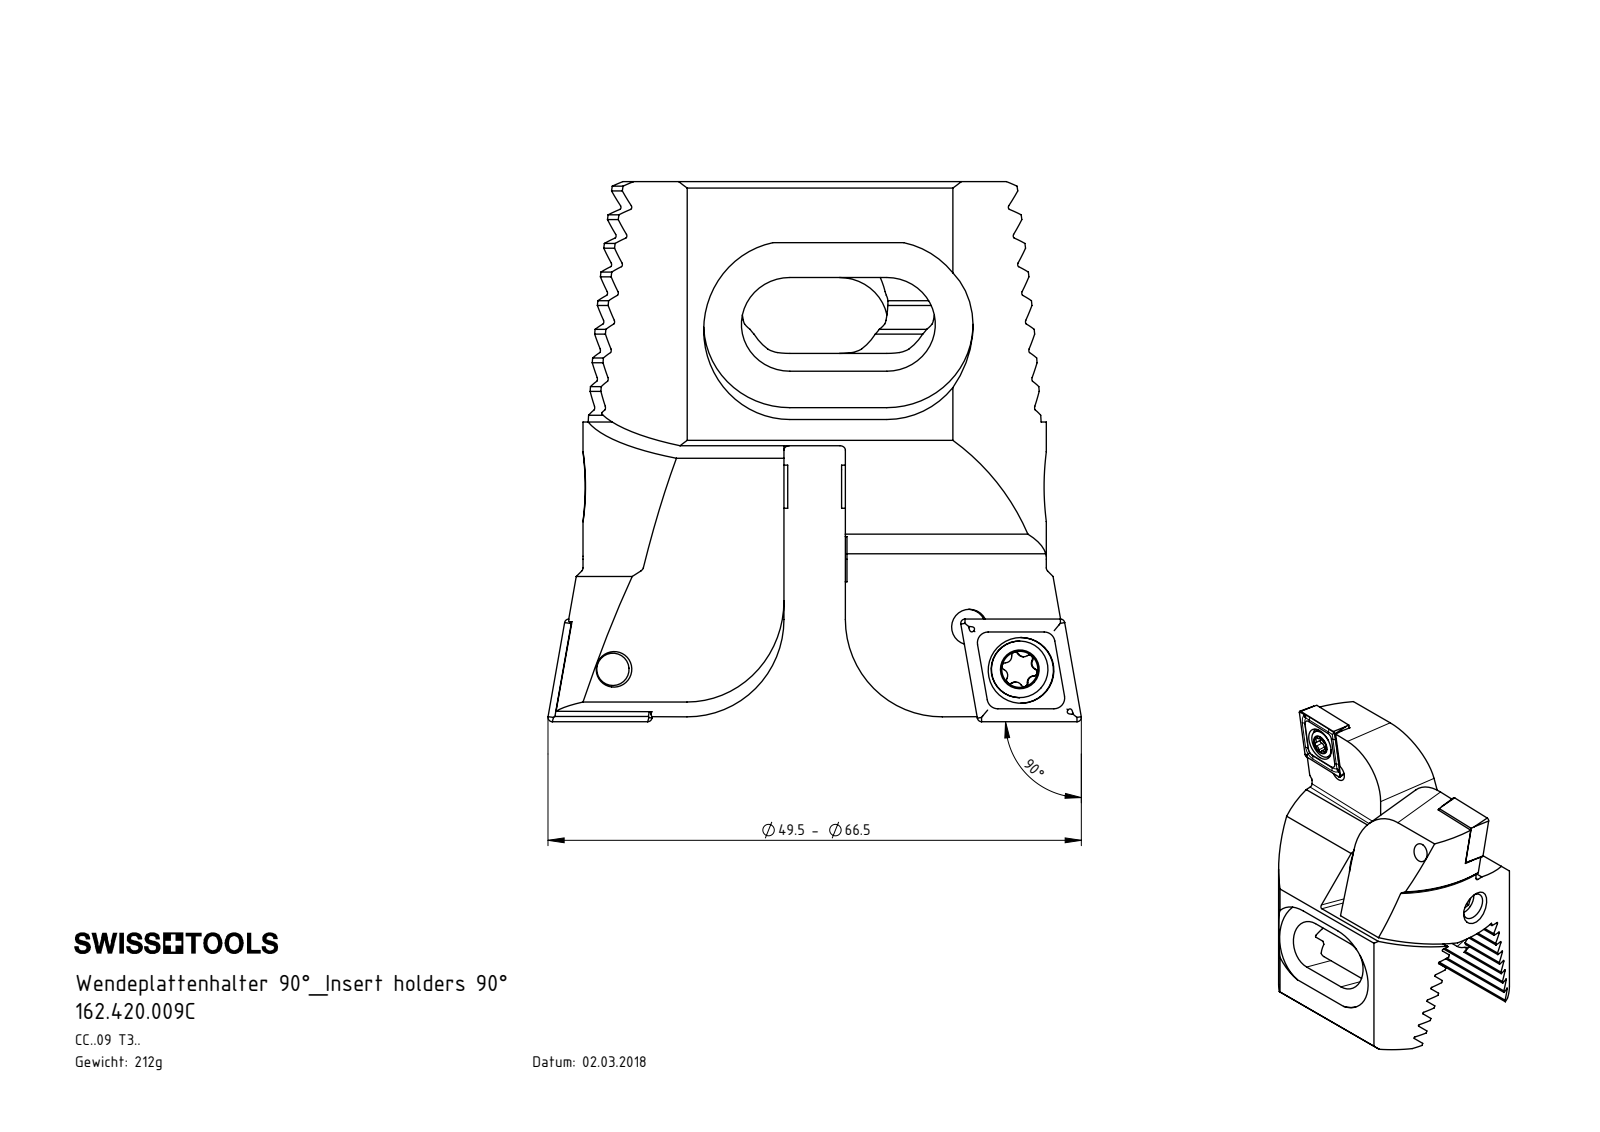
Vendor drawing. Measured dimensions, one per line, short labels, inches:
name: 162.420.009C; Z42-WCB.001.028_A; WCB-ER2.001.009_A; Z42-ER3.001.016 (+1 more)
written by: SolidWorks 2017 (CONFIG_CONTROL_DESIGN)
unit: in
bodies: 8 solids, 460 faces (184 planar, 152 cylindrical, 124 other)
size: 1.972 × 1.949 × 1.346
volume: 1.646 in³; area: 20.87 in²
holes: 4× ⌀0.13, 2× ⌀0.039, 2× ⌀0.173, 2× ⌀0.24, 1× ⌀0.197
bosses: 3× ⌀0.157, 2× ⌀0.207, 1× ⌀0.236
rounds: 16× R0.008, 12× R0.013, 12× R0.023, 8× R0.039, 4× R0.02, 4× R0.177, 4× R0.315, 2× R0.354
face distances: 0.094, 0.187, 0.469, 0.375, 0.563, 0.281, 0.196, 0.281, 0.041, 0.656
hole spacings: 0.24, 0.512, 1.322, 0.246, 0.246, 0.989, 1.13, 1.327
